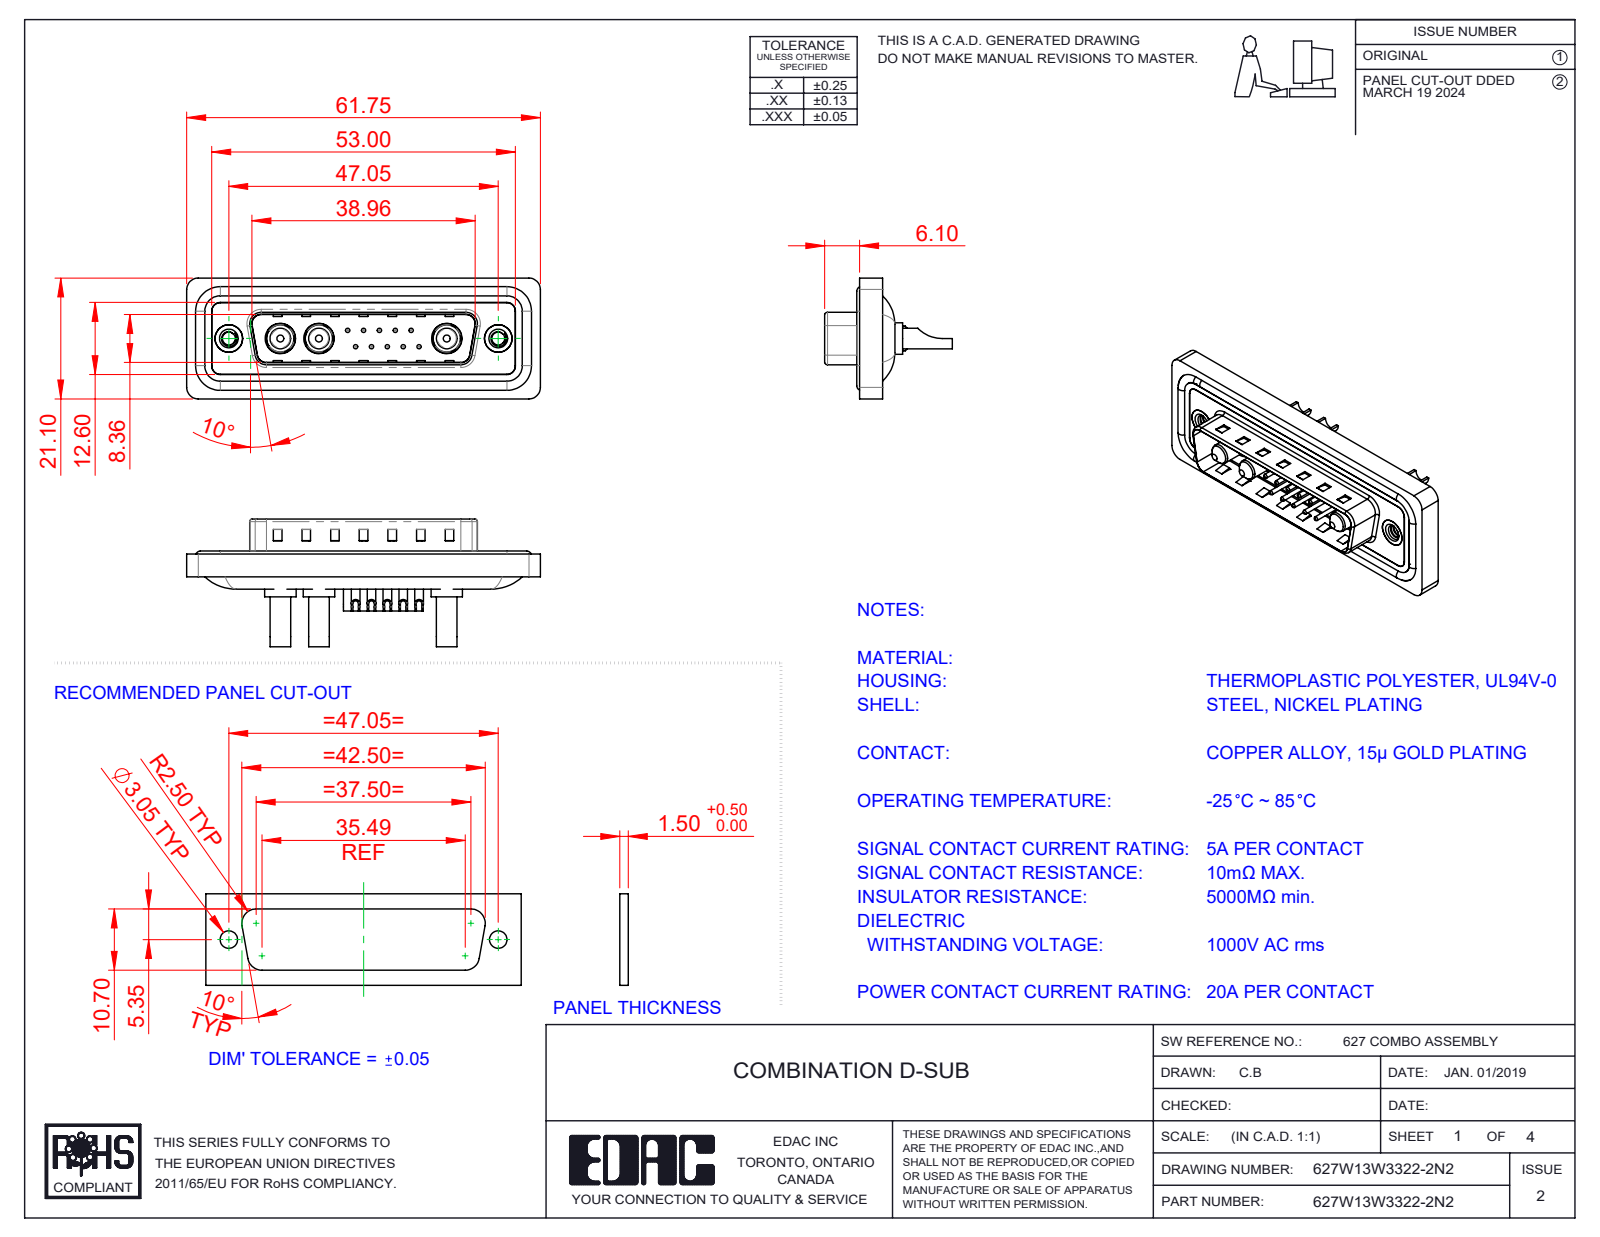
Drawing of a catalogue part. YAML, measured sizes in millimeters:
part_name: "627Combo Contact Row 2_22; 627Combo Shell Front_25 Contacts; 627Combo Housing_13W3; 627W13W3322-2N2 (+5 more)"
step_written_by: "SolidWorks 2023 (CONFIG_CONTROL_DESIGN)"
units: millimeters
bodies: {solids: 23, faces: 991, planar: 338, cylindrical: 414, other: 239}
overall_size: [61.75, 22.3, 21.1]
volume: 7389
surface_area: 12202
round_holes:
  - {diameter: 0.75, count: 10}
  - {diameter: 1, count: 10}
  - {diameter: 1.6, count: 10}
  - {diameter: 2, count: 10}
  - {diameter: 2.7, count: 3}
  - {diameter: 4.85, count: 3}
  - {diameter: 5.3, count: 3}
  - {diameter: 2.26, count: 2}
  - {diameter: 4, count: 2}
  - {diameter: 4.8, count: 2}
  - {diameter: 5, count: 2}
round_bosses_or_shafts:
  - {diameter: 1.5, count: 10}
  - {diameter: 1.6, count: 4}
  - {diameter: 5.5, count: 3}
  - {diameter: 5.2, count: 3}
  - {diameter: 4.75, count: 3}
  - {diameter: 3.75, count: 3}
  - {diameter: 3.6, count: 3}
  - {diameter: 4.9, count: 2}
partial_cylinders:
  - {radius: 1.5, count: 22}
  - {radius: 2, count: 18}
  - {radius: 0.5, count: 8}
  - {radius: 1.6, count: 8}
  - {radius: 1, count: 6}
  - {radius: 0.25, count: 4}
  - {radius: 0.6, count: 4}
  - {radius: 0.65, count: 4}
face_to_face_distances: [0.4, 1.5, 1.1, 1.6, 0.5, 3.1, 2.9, 0.82, 9.58, 4.1]
hole_center_spacings: [3.16, 2.77, 5.04, 5.54, 7.49, 5.03, 8.31, 10.11]
